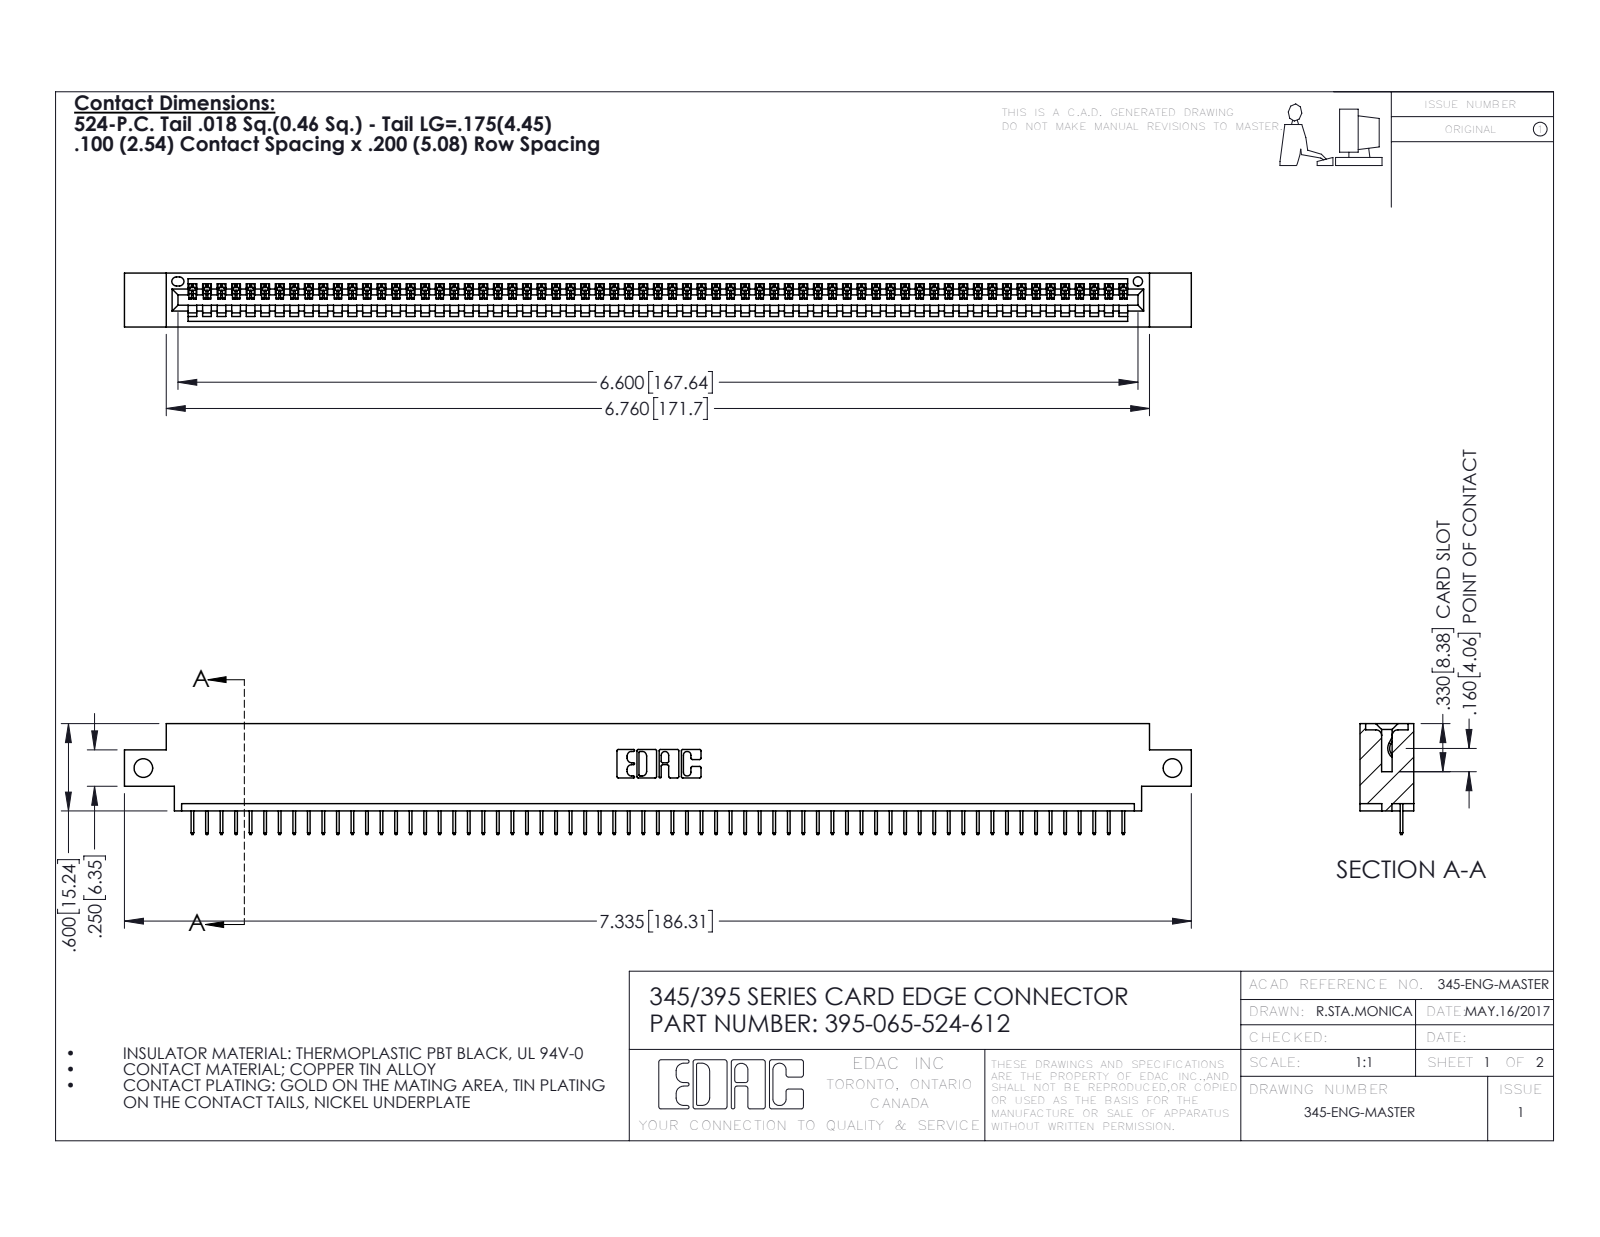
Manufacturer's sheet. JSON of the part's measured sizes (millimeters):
{"part_name": "345 Part_0.170 Offset - Side Mount; 395-065-524-612; 345-292-001_345-293-124", "step_written_by": "SolidWorks 2016 (CONFIG_CONTROL_DESIGN)", "units": "millimeters", "bodies": {"solids": 66, "faces": 4160, "planar": 3074, "cylindrical": 1086, "other": 0}, "overall_size": [186.3, 19.4, 9.4], "volume_mm3": 17420, "surface_area_mm2": 22630, "round_holes": [[3.3, 2], [1.6, 1]], "partial_cylinders_radius": [[0.2, 130], [0.3, 22], [0.2, 6], [0.8, 6], [0.7, 3], [0.8, 2], [1, 2], [0.4, 1]], "face_to_face_distances": [1.8, 7.6, 9.4, 5.1, 2.5, 6.9, 0.6, 5.7, 1.8, 4.4], "hole_center_spacings": [179.7]}
